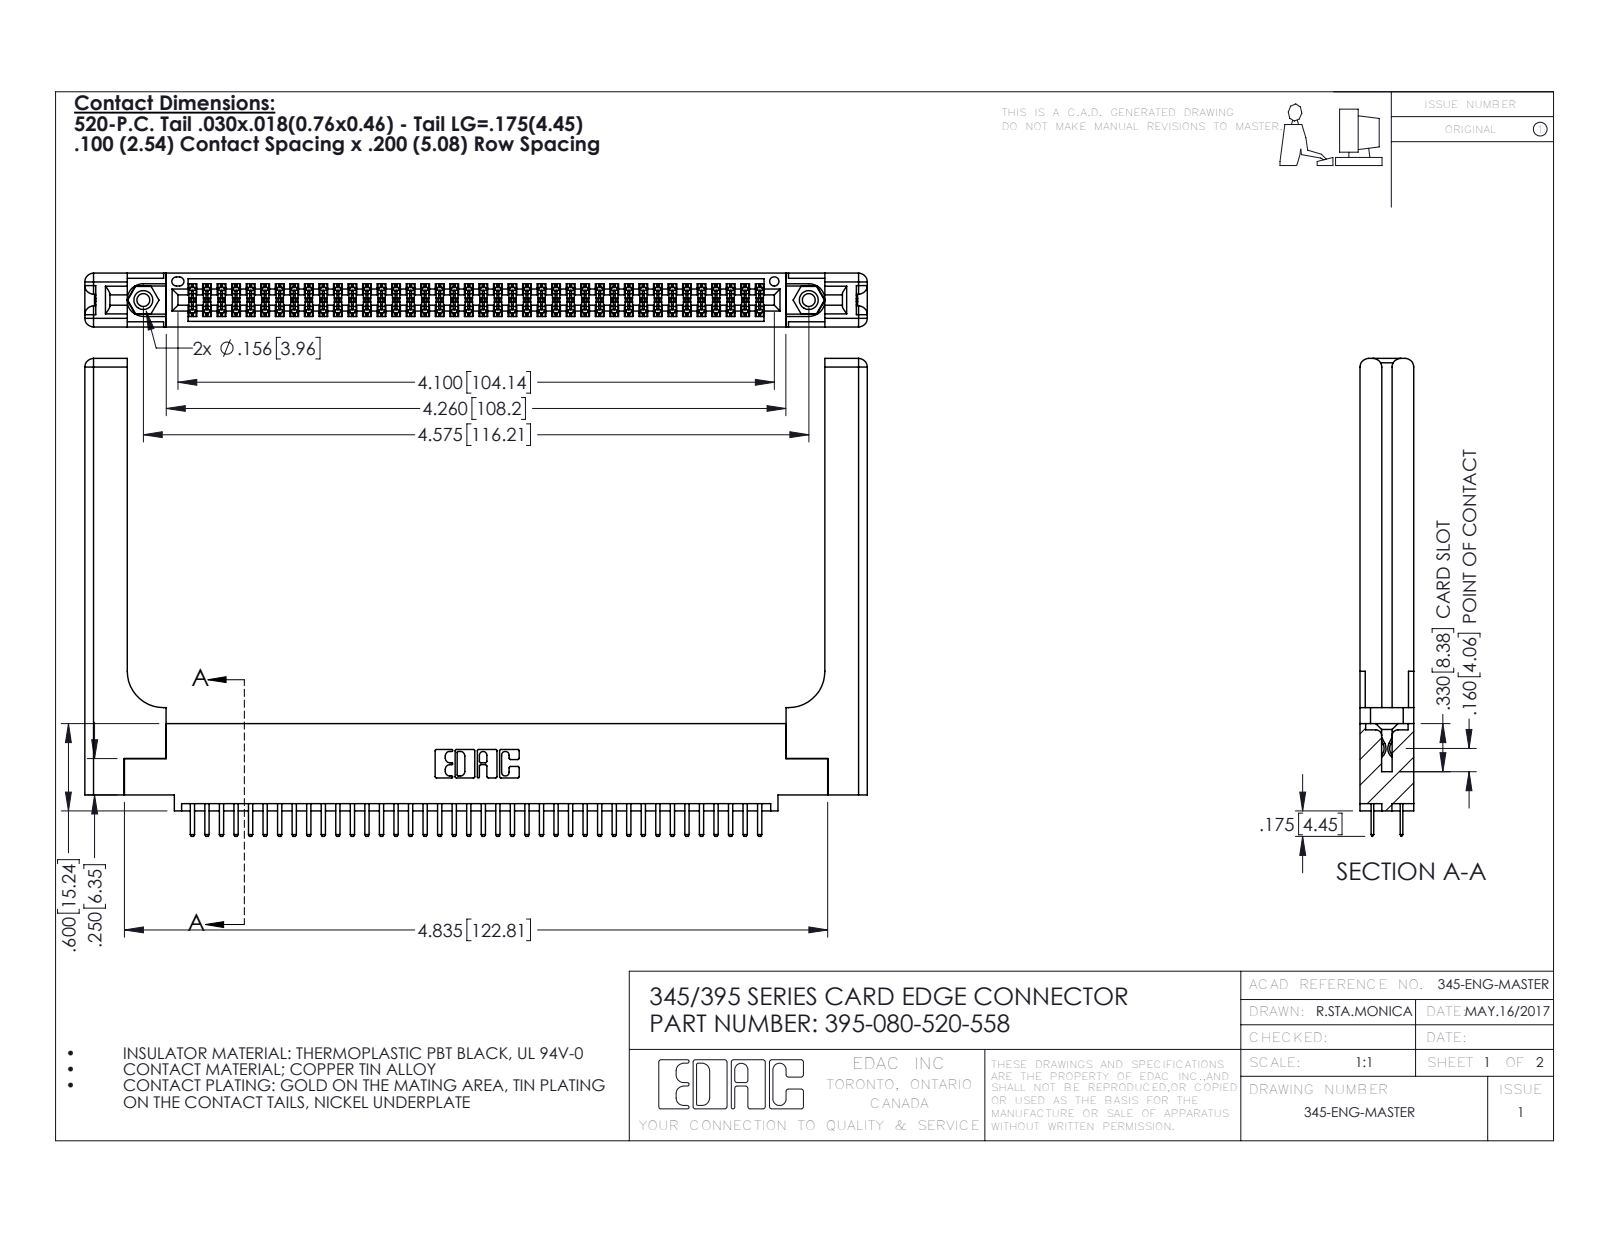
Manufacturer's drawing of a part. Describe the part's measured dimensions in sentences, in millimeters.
The part is named "345-250-001_345-250-001-102; 395-080-520-558; 345-292-001_345-293-120; 345 Part_0.110 Offset - 0.156 Dia-TH (+1 more)". Its 3-D file was written by "SolidWorks 2016 (CONFIG_CONTROL_DESIGN)". It is 85 solids with 4706 faces: 3032 planar, 1614 cylindrical and 60 other. Overall it measures 136.6 by 83.4 by 9.4 millimeters. Its volume is 21 610 cubic millimeters and its surface area 24 470 square millimeters. Round holes: 2 of diameter 2.3, 2 of diameter 3.2, 2 of diameter 4, 1 of diameter 1.6. Round bosses or shafts: 2 of diameter 3.9. Partial cylindrical surfaces (rounded edges, fillets, slot ends): 120 of radius 0.2, 84 of radius 0.3, 22 of radius 0.3, 16 of radius 1.5, 6 of radius 0.2, 6 of radius 0.8, 3 of radius 0.7, 2 of radius 0.4. The main face-to-face distances are 9.4, 1.8, 7.6, 5.1, 2.5, 6.9, 0.6, 5.7, 3.8, 3.8. The hole center spacings are 6.9, 110.2, 116.2.
